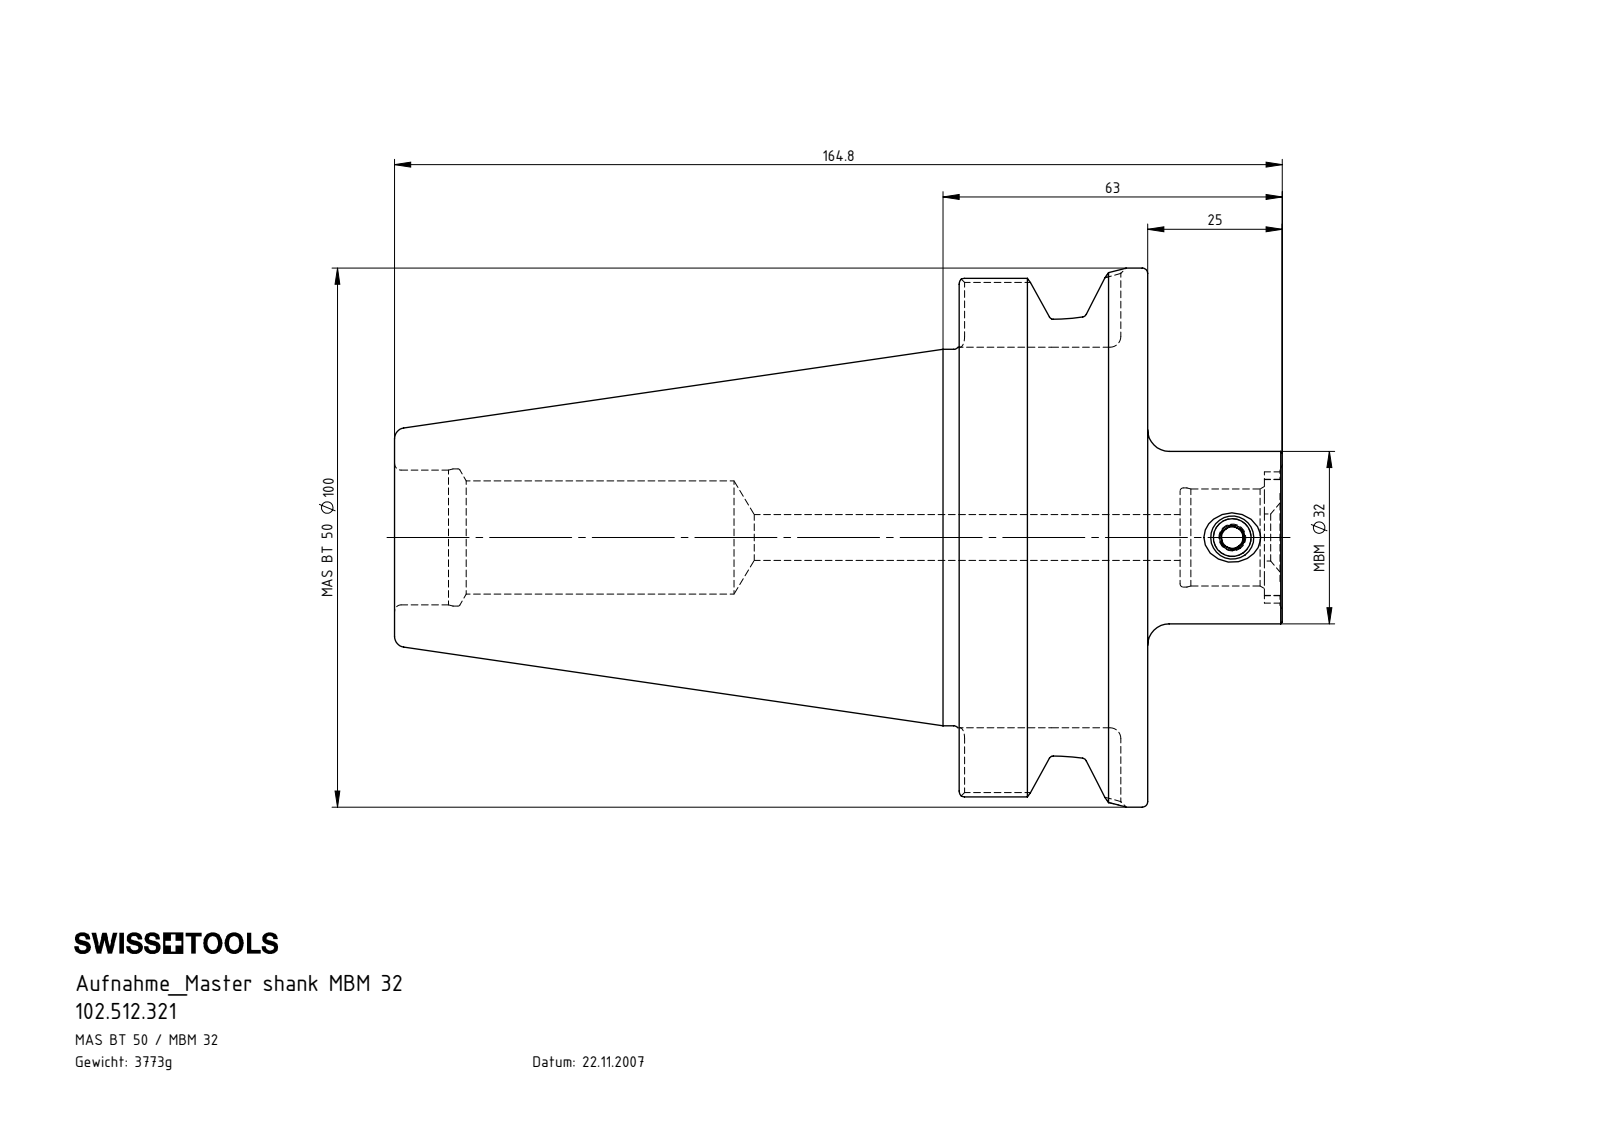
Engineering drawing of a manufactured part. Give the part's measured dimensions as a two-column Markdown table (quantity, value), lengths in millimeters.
| quantity | value |
| --- | --- |
| part name | BB5-MB3.K01.063_C; 102.512.321; ISO 4026 - M5 x 5_PreviewCfg; ISO 4026 - M6 x 5_PreviewCfg (+1 more) |
| STEP written by | SolidWorks 2017 (CONFIG_CONTROL_DESIGN) |
| units | millimeters |
| bodies | 6 solids, 234 faces (79 planar, 70 cylindrical, 85 other) |
| overall size | 164.8 × 100 × 100 |
| volume | 478 858 mm³ |
| surface area | 56 742 mm² |
| round holes (diameter × count) | 4.2 × 2, 6 × 2, 4 × 1, 5 × 1, 7 × 1, 8.5 × 1, 18 × 1, 18.4 × 1, 21 × 1, 25 × 1, 25.45 × 1 |
| round bosses / shafts (diameter × count) | 6 × 2, 5 × 2, 100 × 1, 85 × 1, 69.85 × 1, 32 × 1, 8 × 1 |
| partial cylindrical surfaces (radius × count) | 2 × 8, 3.2 × 4, 12.18 × 1, 12.85 × 1 |
| main face-to-face distances | 35, 70.6, 104.8, 139.8, 25.7, 164.8, 60, 25, 145.8, 41 |
